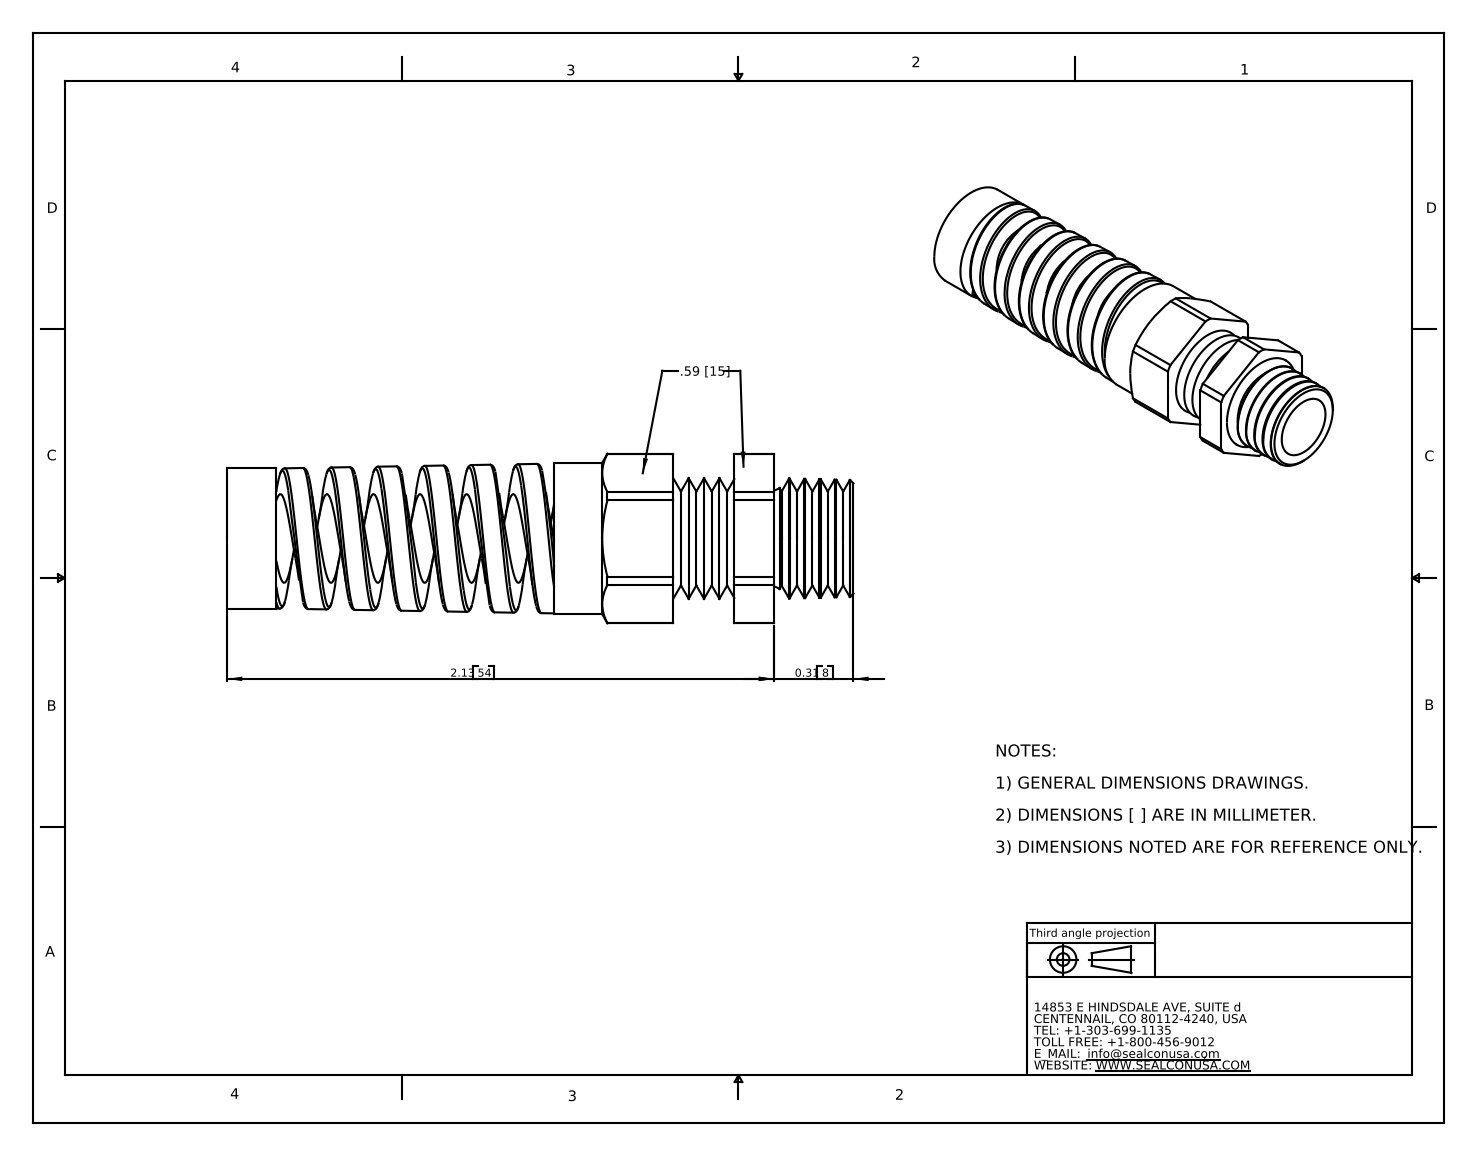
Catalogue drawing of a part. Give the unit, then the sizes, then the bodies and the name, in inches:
Units: inches
Overall size (bounding box): 2.44 × 0.661 × 0.59
Round holes (diameter × count): ⌀0.26 ×1, ⌀0.346 ×1, ⌀0.47 ×1
Round bosses / shafts (diameter × count): ⌀0.59 ×1, ⌀0.546 ×1
Partial cylindrical surfaces — rounded edges, fillets, slot ends (radius × count): R0.33 ×1
Main face-to-face distances: 0.59, 1.976, 1.738, 0.238, 1.274, 0.464, 0.702, 2.13, 0.856, 0.392
Volume: 0.3 in³ · Surface area: 8.515 in²
Bodies: 1 solid, 131 faces (19 planar, 34 cylindrical, 78 other)
Part name (STEP PRODUCT): CF12MA
STEP written by: SolidWorks 2007 (CONFIG_CONTROL_DESIGN)
